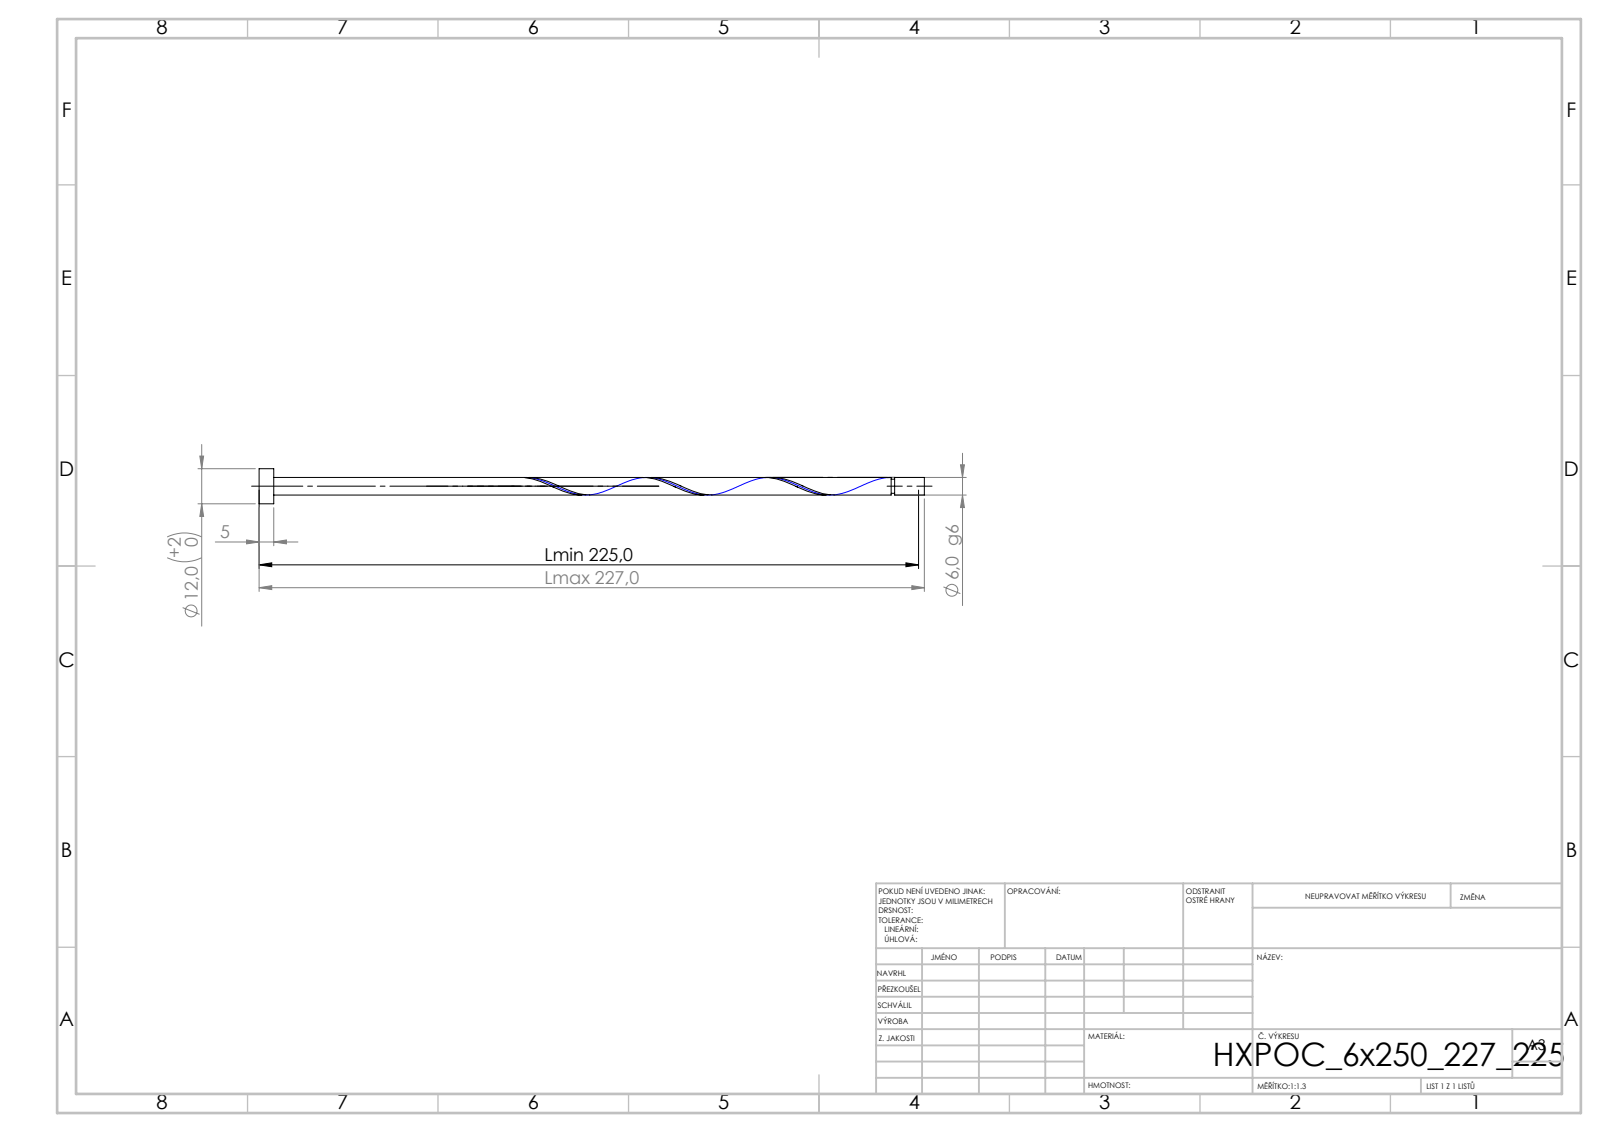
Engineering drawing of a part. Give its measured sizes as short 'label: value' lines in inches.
written by: SolidWorks 2019 (CONFIG_CONTROL_DESIGN)
unit: in
bodies: 1 solid, 21 faces (6 planar, 14 cylindrical, 1 other)
size: 8.937 × 0.472 × 0.472
volume: 0.413 in³; area: 7.279 in²
bosses: 1× ⌀0.472, 1× ⌀0.236, 1× ⌀0.189
face distances: 0.197, 8.937, 8.74, 8.538, 8.341, 0.399, 8.491, 8.294, 0.047, 0.446
